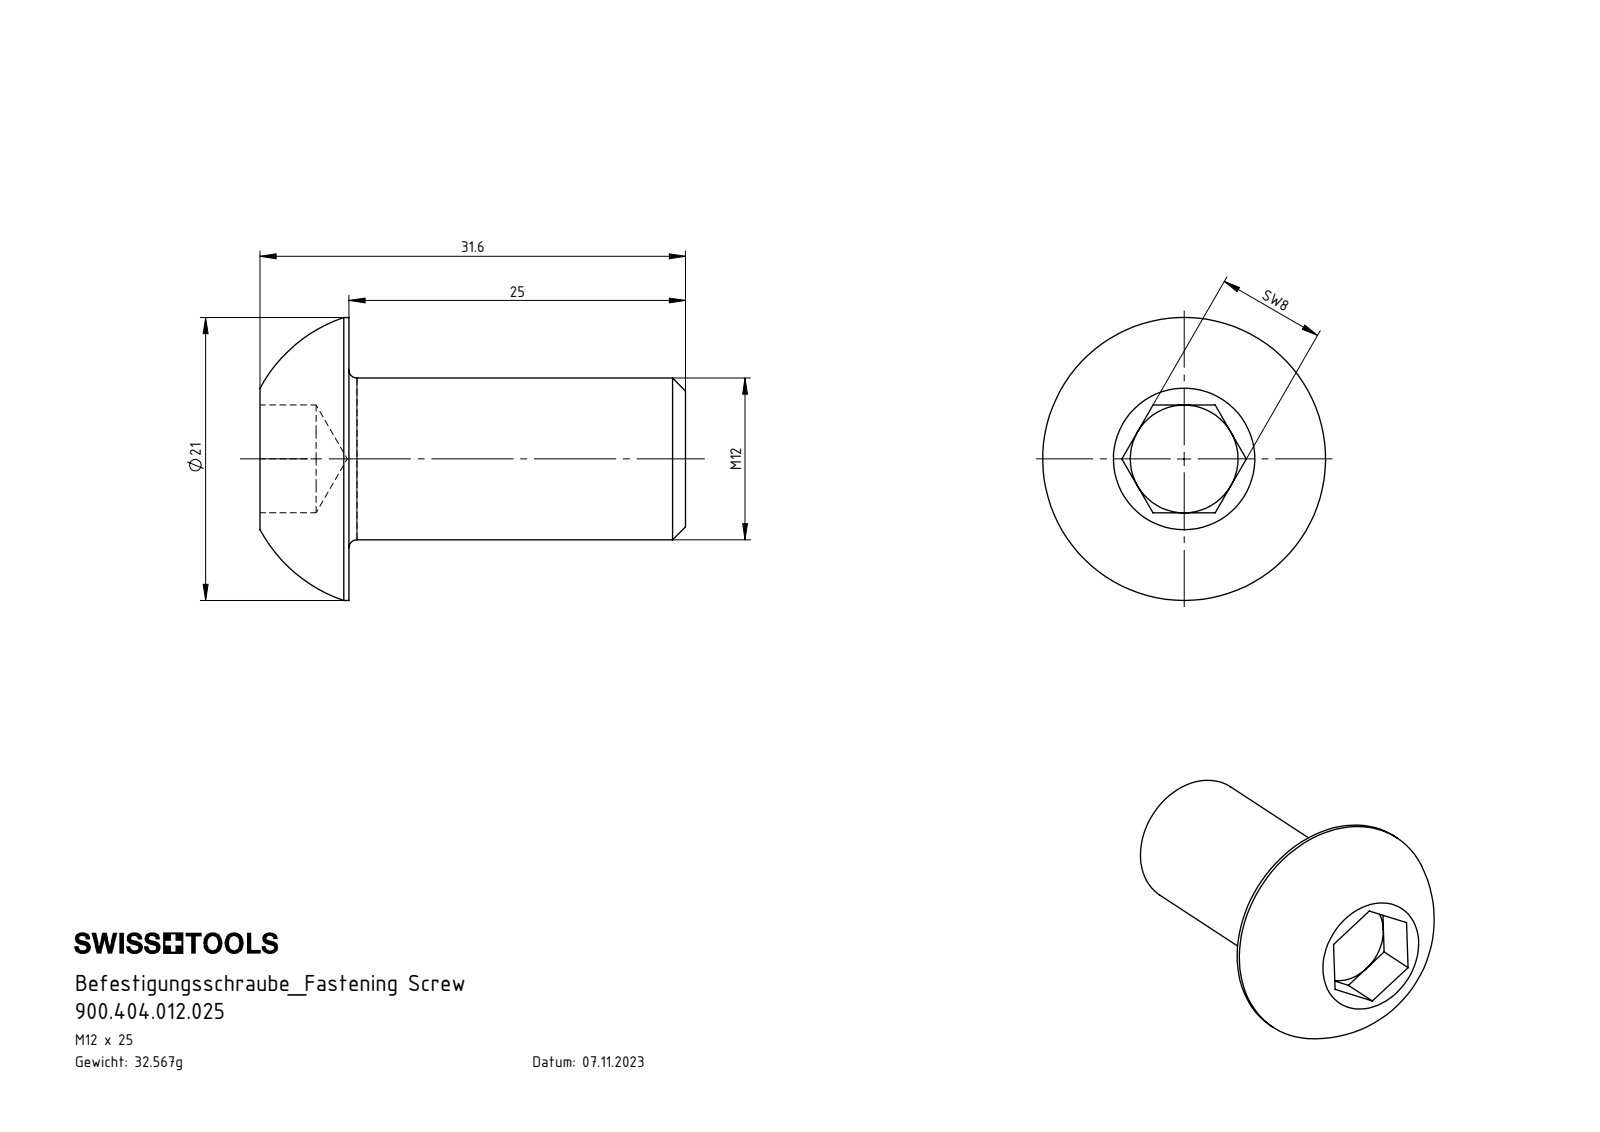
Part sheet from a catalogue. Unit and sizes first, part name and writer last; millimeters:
Units: millimetres
Overall size (bounding box): 31.6 × 21 × 21
Round bosses / shafts (diameter × count): ⌀21 ×1, ⌀12 ×1
Main face-to-face distances: 25, 8, 6.6, 31.6, 4.16, 2.44, 27.44
Volume: 4 149 mm³ · Surface area: 1 925 mm²
Bodies: 1 solid, 27 faces (15 planar, 4 cylindrical, 8 other)
Part name (STEP PRODUCT): 900.404.012.025
STEP written by: SolidWorks 2022 (AUTOMOTIVE_DESIGN)
